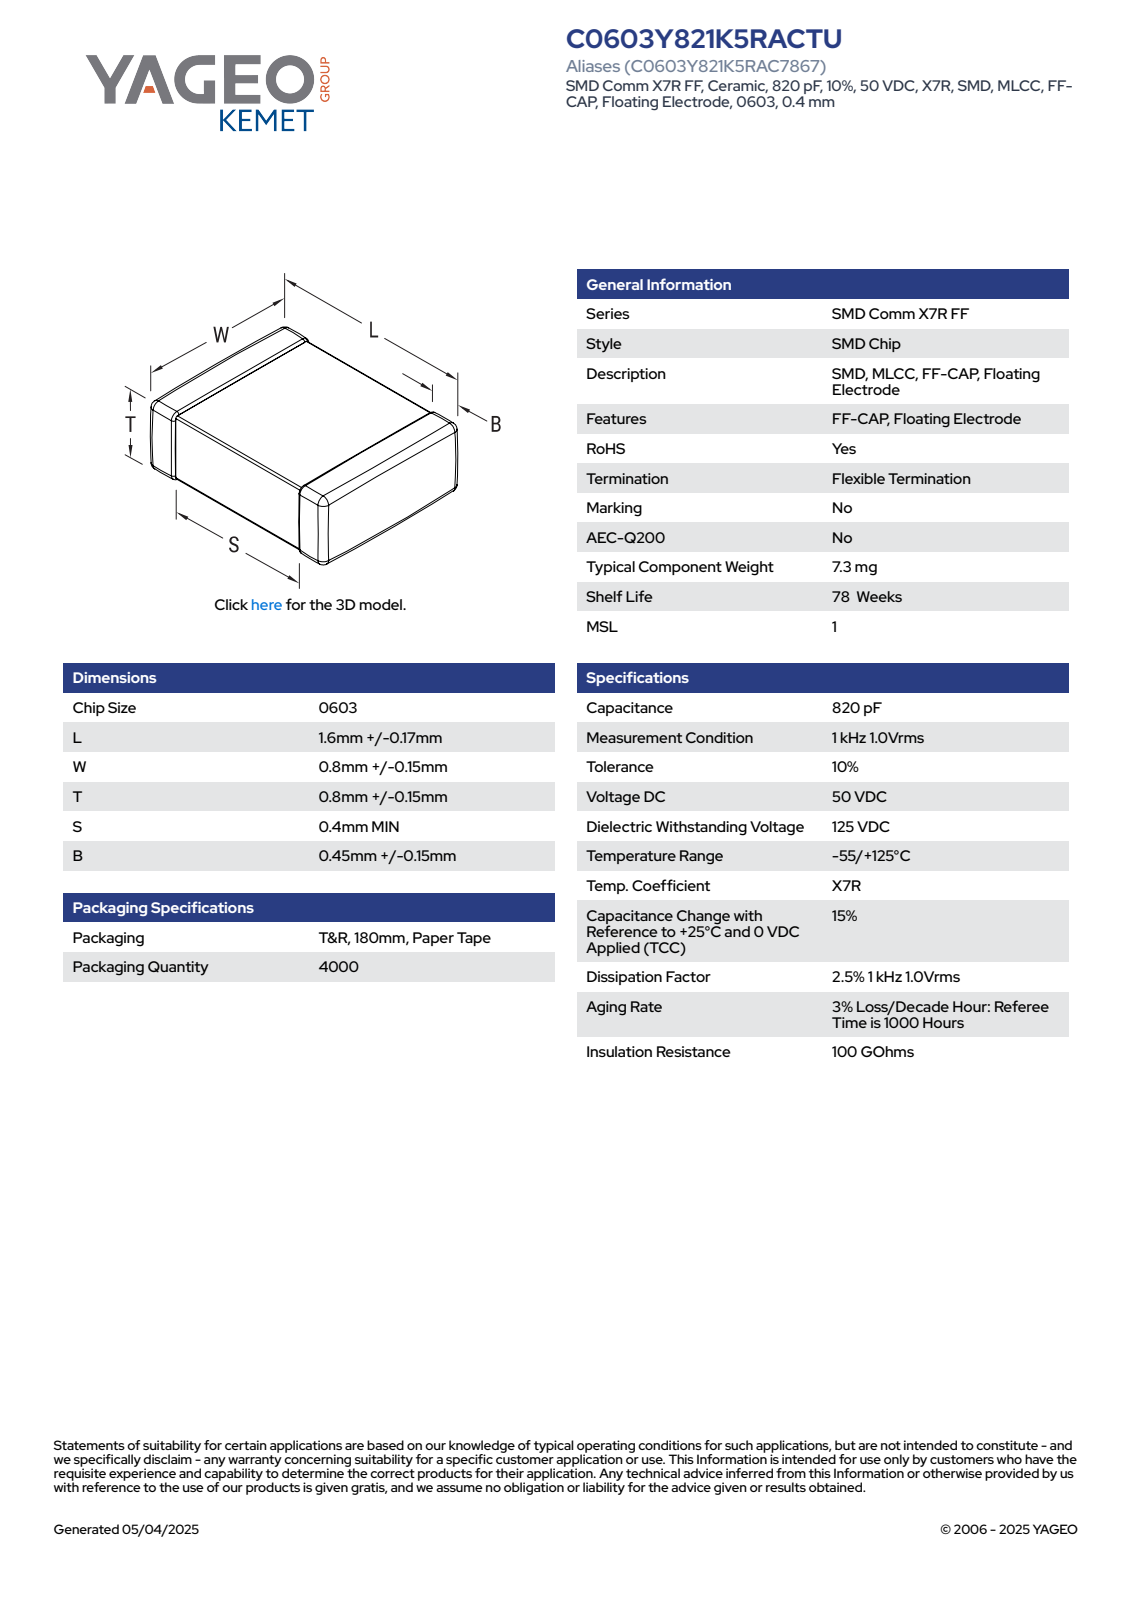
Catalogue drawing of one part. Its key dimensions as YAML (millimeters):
part_name: "CCS_CCSTD_0603_L1.77W0.95T0.95B0.45"
step_written_by: "SolidWorks 2014 (AUTOMOTIVE_DESIGN)"
units: millimeters
bodies: {solids: 4, faces: 125, planar: 71, cylindrical: 38, other: 16}
overall_size: [1.77, 0.95, 0.95]
volume: 2
surface_area: 8
face_to_face_distances: [0.93, 0.91, 0.95, 1.77, 0.94, 0.92, 0.82, 0.96, 0.81, 0.84]
